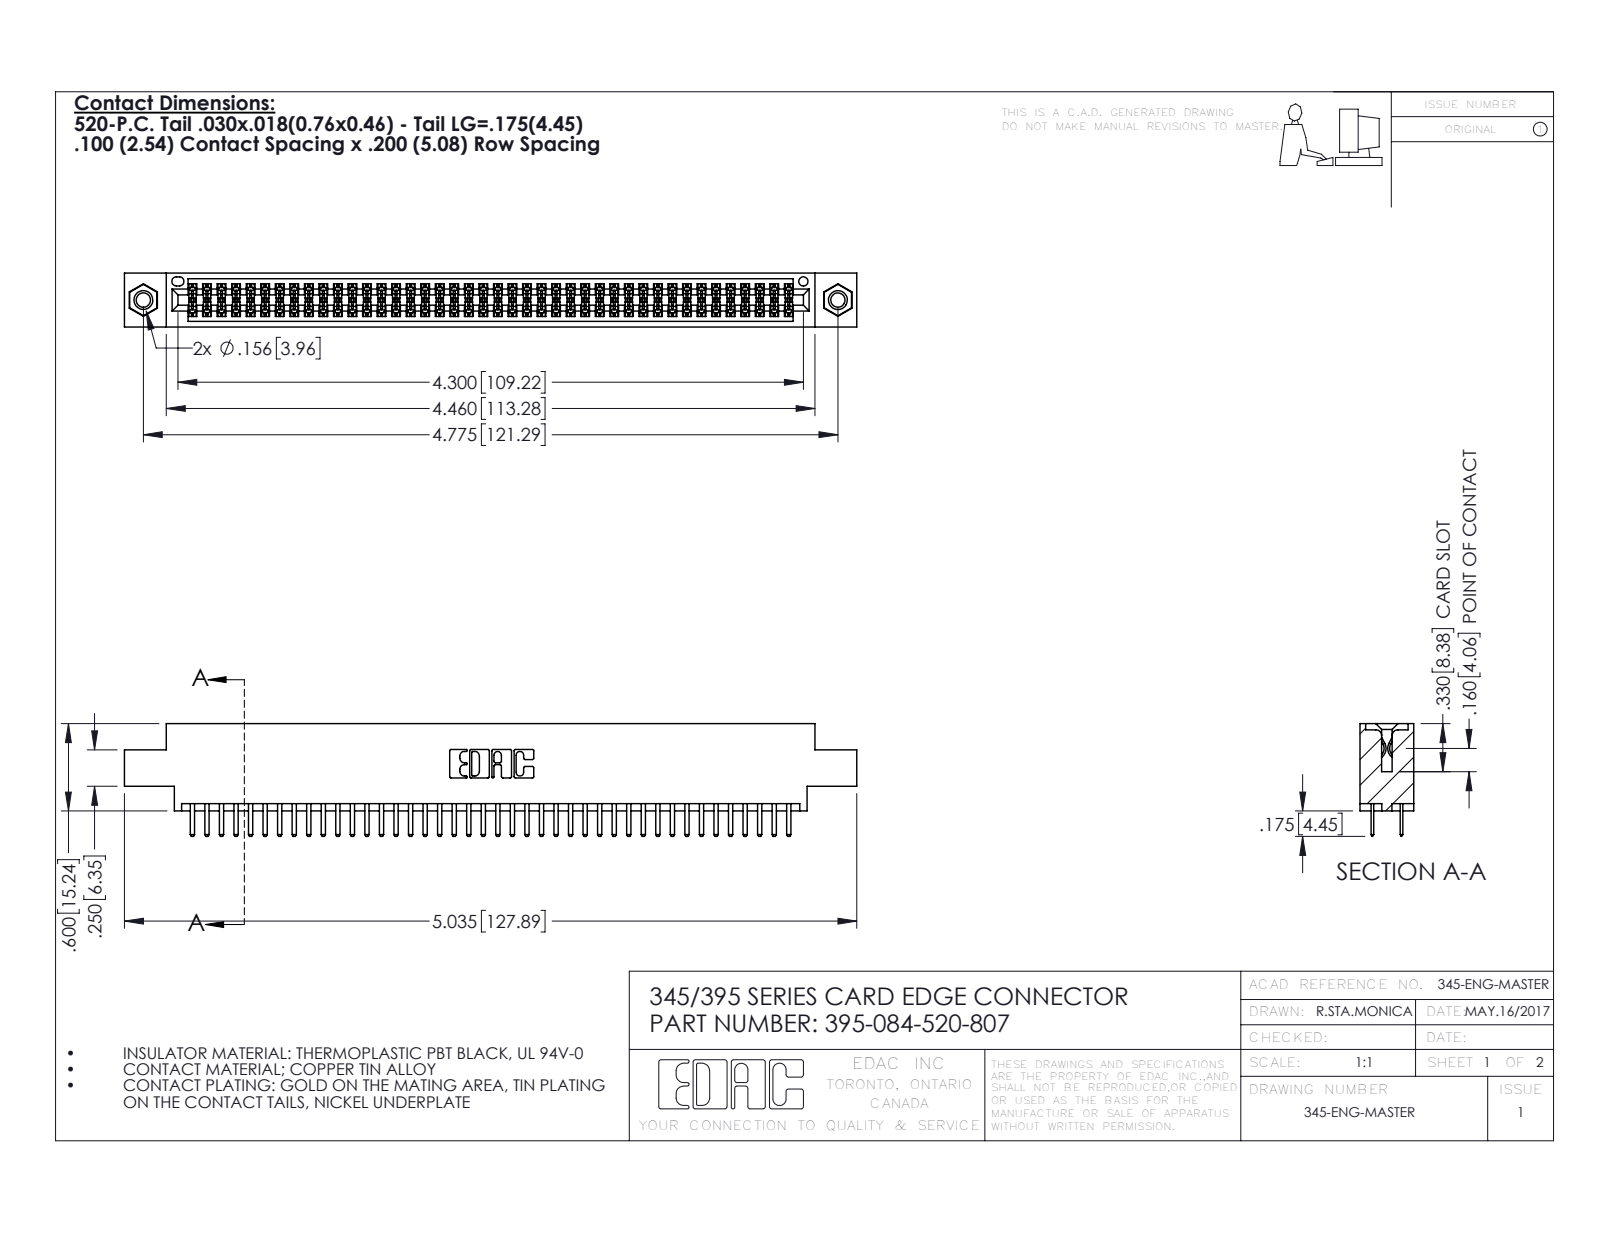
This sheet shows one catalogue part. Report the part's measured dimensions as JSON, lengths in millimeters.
{"part_name": "395-084-520-807; 345 Part_0.170 Offset - 0.156 Dia-TI; 345-250-001_345-250-005-103; 345-292-001_345-293-120", "step_written_by": "SolidWorks 2016 (CONFIG_CONTROL_DESIGN)", "units": "millimeters", "bodies": {"solids": 87, "faces": 4726, "planar": 3056, "cylindrical": 1654, "other": 16}, "overall_size": [127.9, 19.7, 9.4], "volume_mm3": 12300, "surface_area_mm2": 18210, "round_holes": [[2.5, 2], [3.2, 2], [4, 2], [1.6, 1]], "round_bosses_or_shafts": [[3.9, 2]], "partial_cylinders_radius": [[0.2, 126], [0.3, 88], [0.3, 22], [0.2, 6], [0.8, 6], [0.7, 3], [0.4, 2], [0.5, 2]], "face_to_face_distances": [1.8, 7.6, 5.1, 9.4, 2.5, 6.9, 0.6, 5.7, 0.6, 4.4], "hole_center_spacings": [6.9, 115.3, 121.3]}
